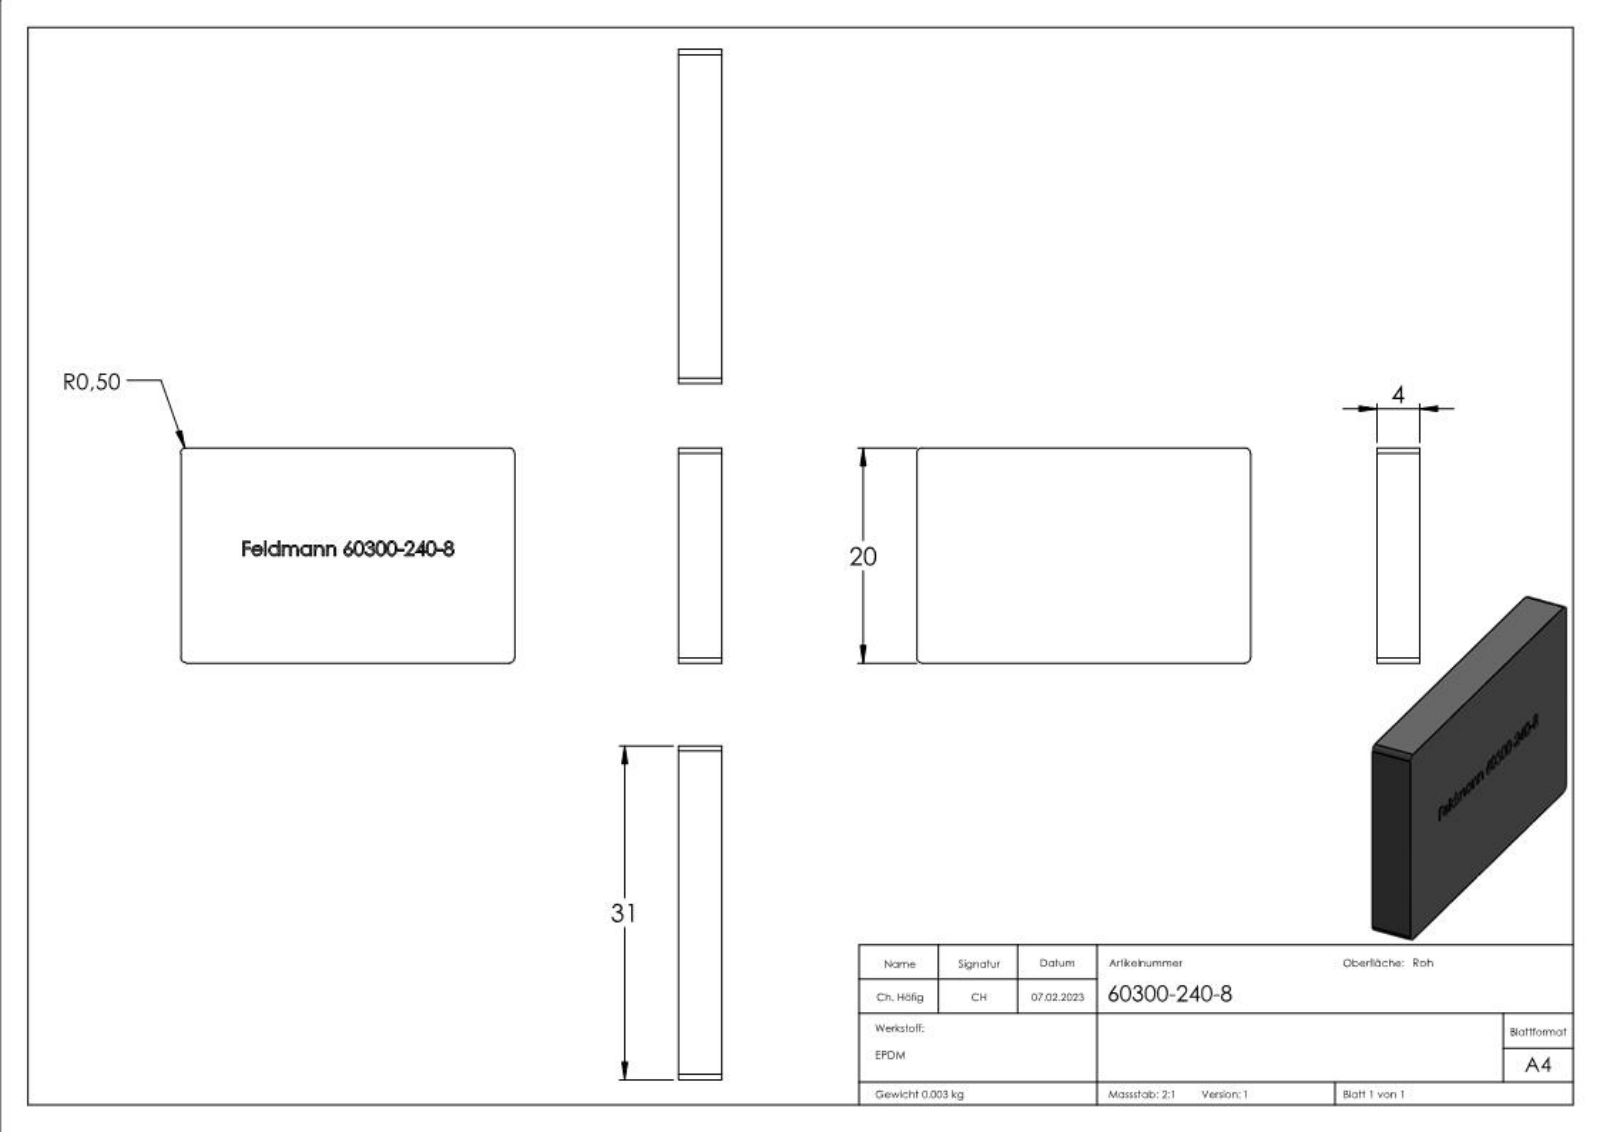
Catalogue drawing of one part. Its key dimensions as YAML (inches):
part_name: "60300-240-8"
step_written_by: "SolidWorks 2015 (CONFIG_CONTROL_DESIGN)"
units: inches
bodies: {solids: 1, faces: 257, planar: 123, cylindrical: 4, other: 130}
overall_size: [1.22, 0.787, 0.157]
volume: 0.151
surface_area: 2.632
partial_cylinders:
  - {radius: 0.02, count: 4}
face_to_face_distances: [0.157, 0.787, 1.22, 0.02, 0.138, 0.394, 0.015, 0.117, 0.017, 0.08]
